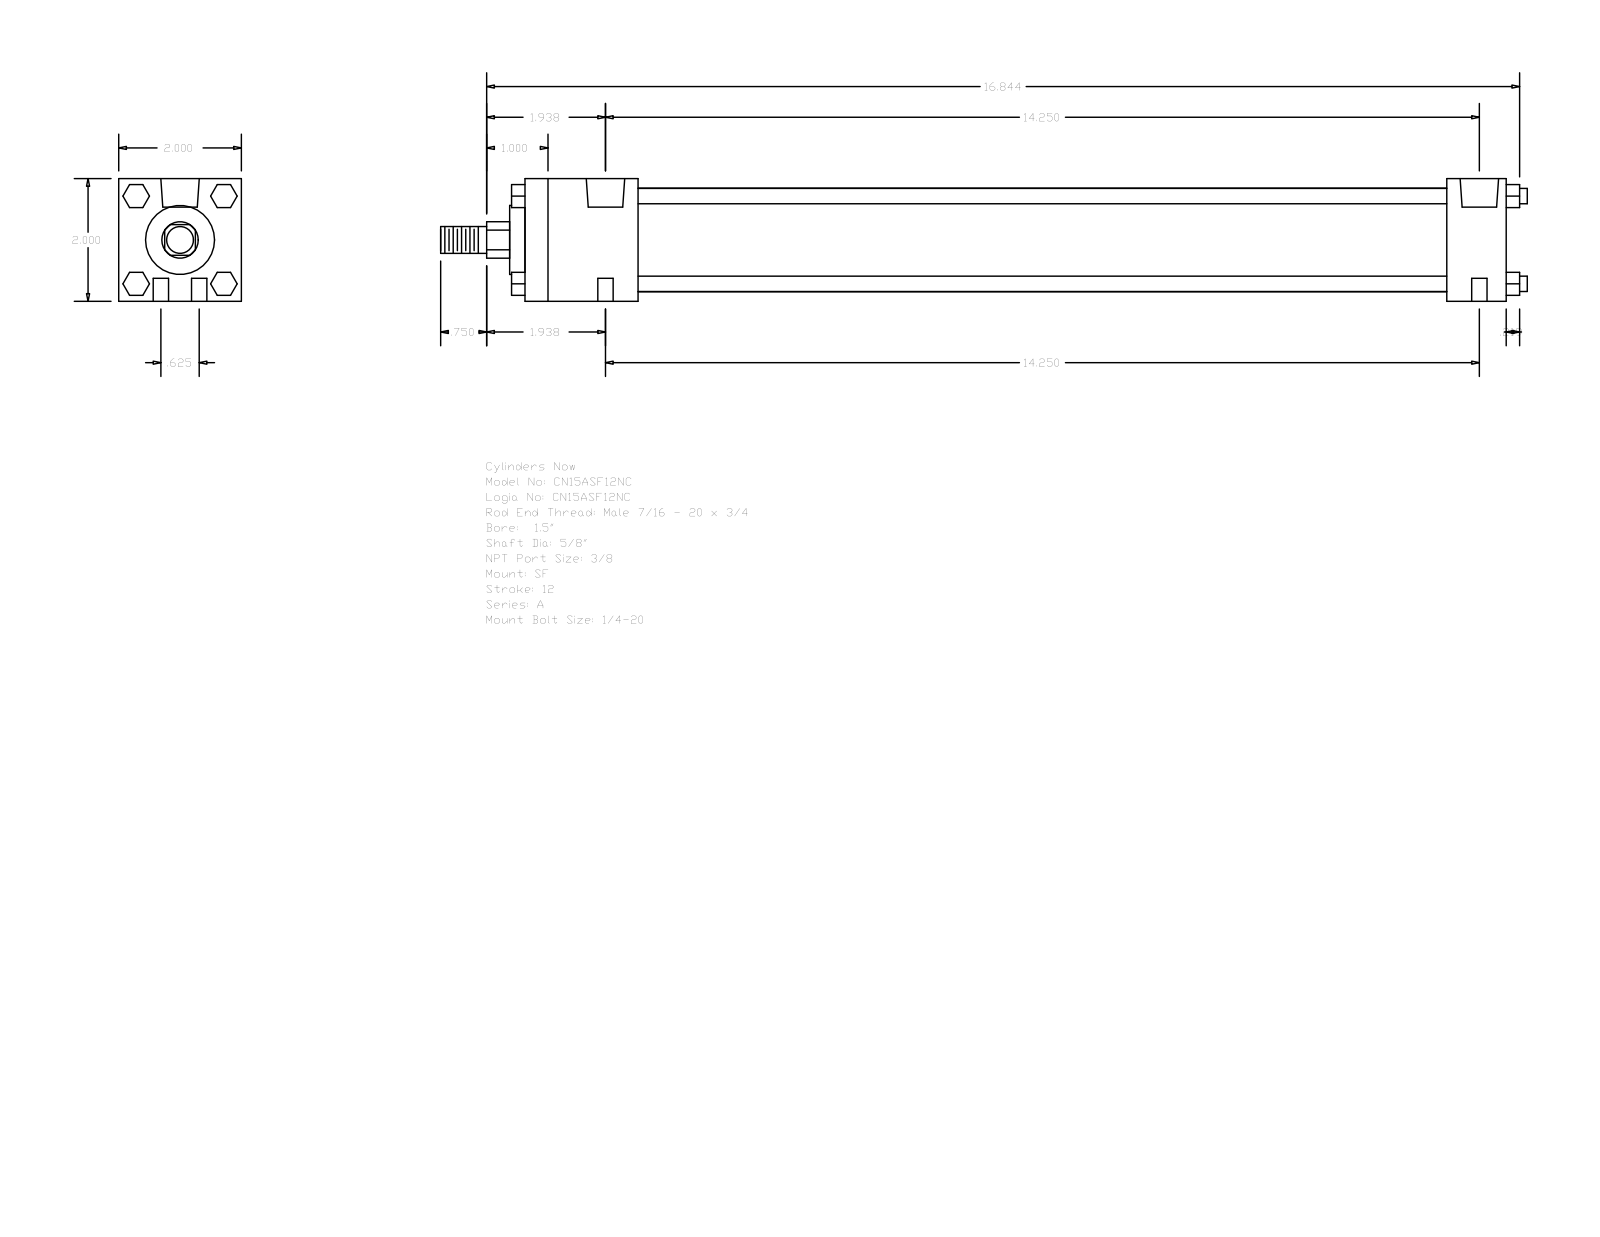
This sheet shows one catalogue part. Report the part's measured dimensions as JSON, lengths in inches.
{"part_name": "A_SF__0150_0.625", "step_written_by": "GSSL Pune (CONFIG_CONTROL_DESIGN)", "units": "inches", "bodies": {"solids": 0, "faces": 124, "planar": 94, "cylindrical": 30, "other": 0}, "overall_size": [17.719, 2, 2], "round_holes": [[0.25, 4], [0.219, 2], [0.627, 2]], "round_bosses_or_shafts": [[0.25, 4], [1.69, 1], [1.125, 1], [0.625, 1], [0.437, 1]], "partial_cylinders_radius": [[0.297, 1]], "face_to_face_distances": [2, 16, 1.844, 15.031, 13.187, 14.156, 0.969, 0.25, 0.375, 2.094], "hole_center_spacings": [0.313, 14.254, 14.25, 0.625, 14.264, 13.937]}
